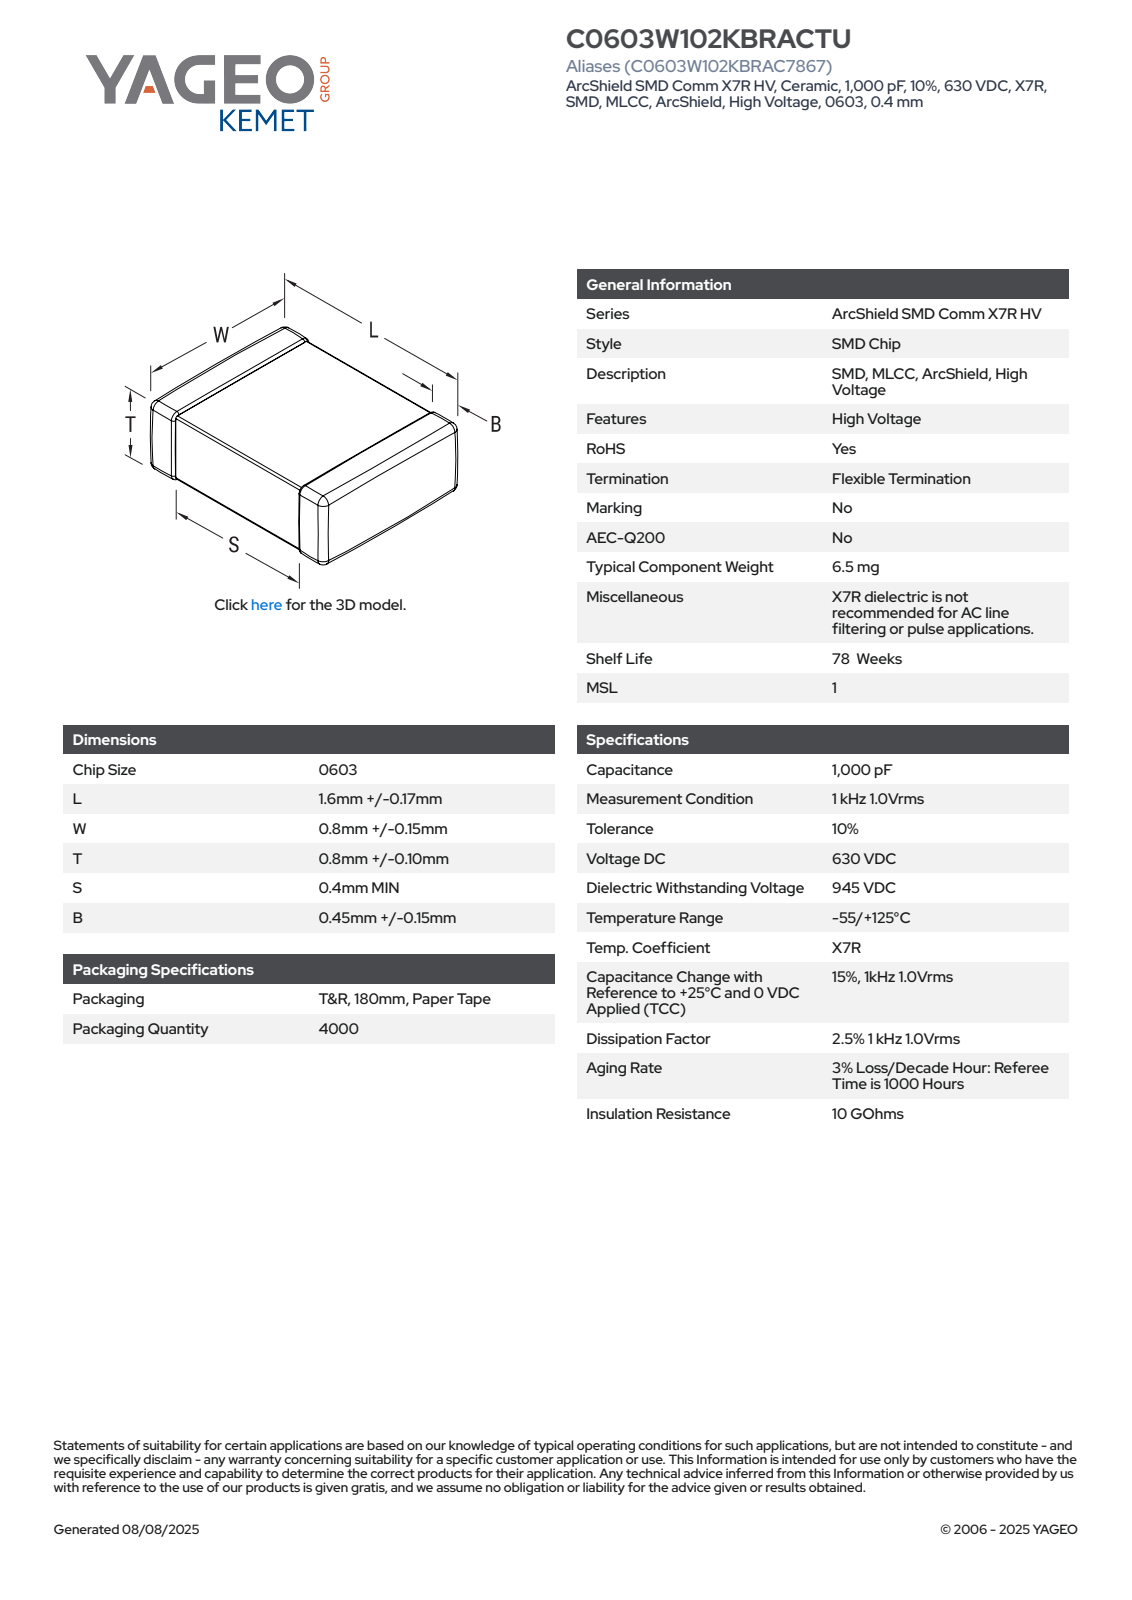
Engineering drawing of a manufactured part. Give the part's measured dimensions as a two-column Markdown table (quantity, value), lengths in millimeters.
| quantity | value |
| --- | --- |
| part name | CCS_CCSTD_0603_L1.77W0.95T0.9B0.45 |
| STEP written by | SolidWorks 2014 (AUTOMOTIVE_DESIGN) |
| units | millimeters |
| bodies | 4 solids, 125 faces (71 planar, 38 cylindrical, 16 other) |
| overall size | 1.77 × 0.95 × 0.9 |
| volume | 1 mm³ |
| surface area | 8 mm² |
| main face-to-face distances | 0.88, 0.93, 1.77, 0.86, 0.9, 0.91, 0.95, 0.87, 0.89, 0.82 |
